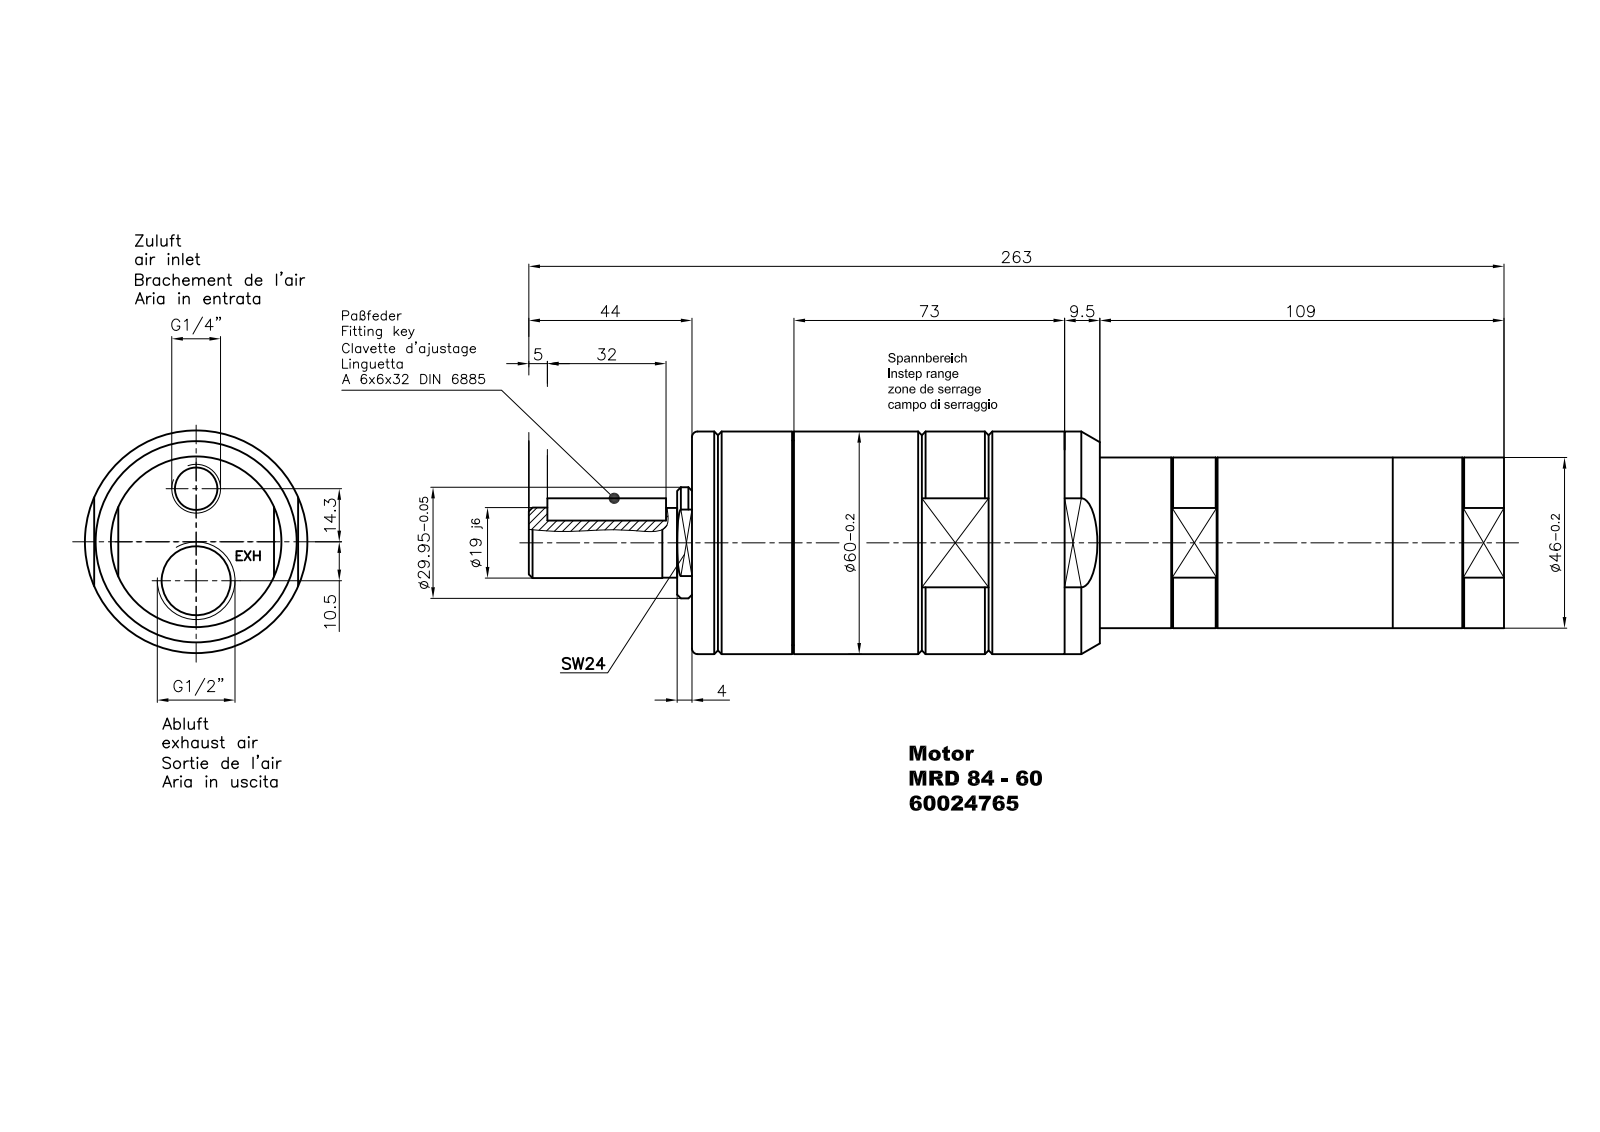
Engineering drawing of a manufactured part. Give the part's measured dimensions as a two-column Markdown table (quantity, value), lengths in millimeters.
| quantity | value |
| --- | --- |
| part name | MRD 84-263 |
| STEP written by | Autodesk Inventor 2012 (AUTOMOTIVE_DESIGN) |
| units | millimeters |
| bodies | 1 solid, 149 faces (83 planar, 34 cylindrical, 32 other) |
| overall size | 263 × 60 × 60 |
| volume | 494 766 mm³ |
| surface area | 51 823 mm² |
| round holes (diameter × count) | 1.55 × 1, 1.6 × 1, 5.5 × 1, 11.45 × 1, 18.63 × 1, 20 × 1, 35 × 1, 46.5 × 1 |
| round bosses / shafts (diameter × count) | 60 × 1, 55.16 × 1, 46 × 1, 29.95 × 1, 19 × 1, 18.8 × 1, 5 × 1 |
| partial cylindrical surfaces (radius × count) | 3 × 2 |
| main face-to-face distances | 100.5, 219, 118.5, 6.5, 109, 55, 104.5, 110, 9.5, 30 |
| hole center spacings | 10.5, 14.3, 24.8 |
